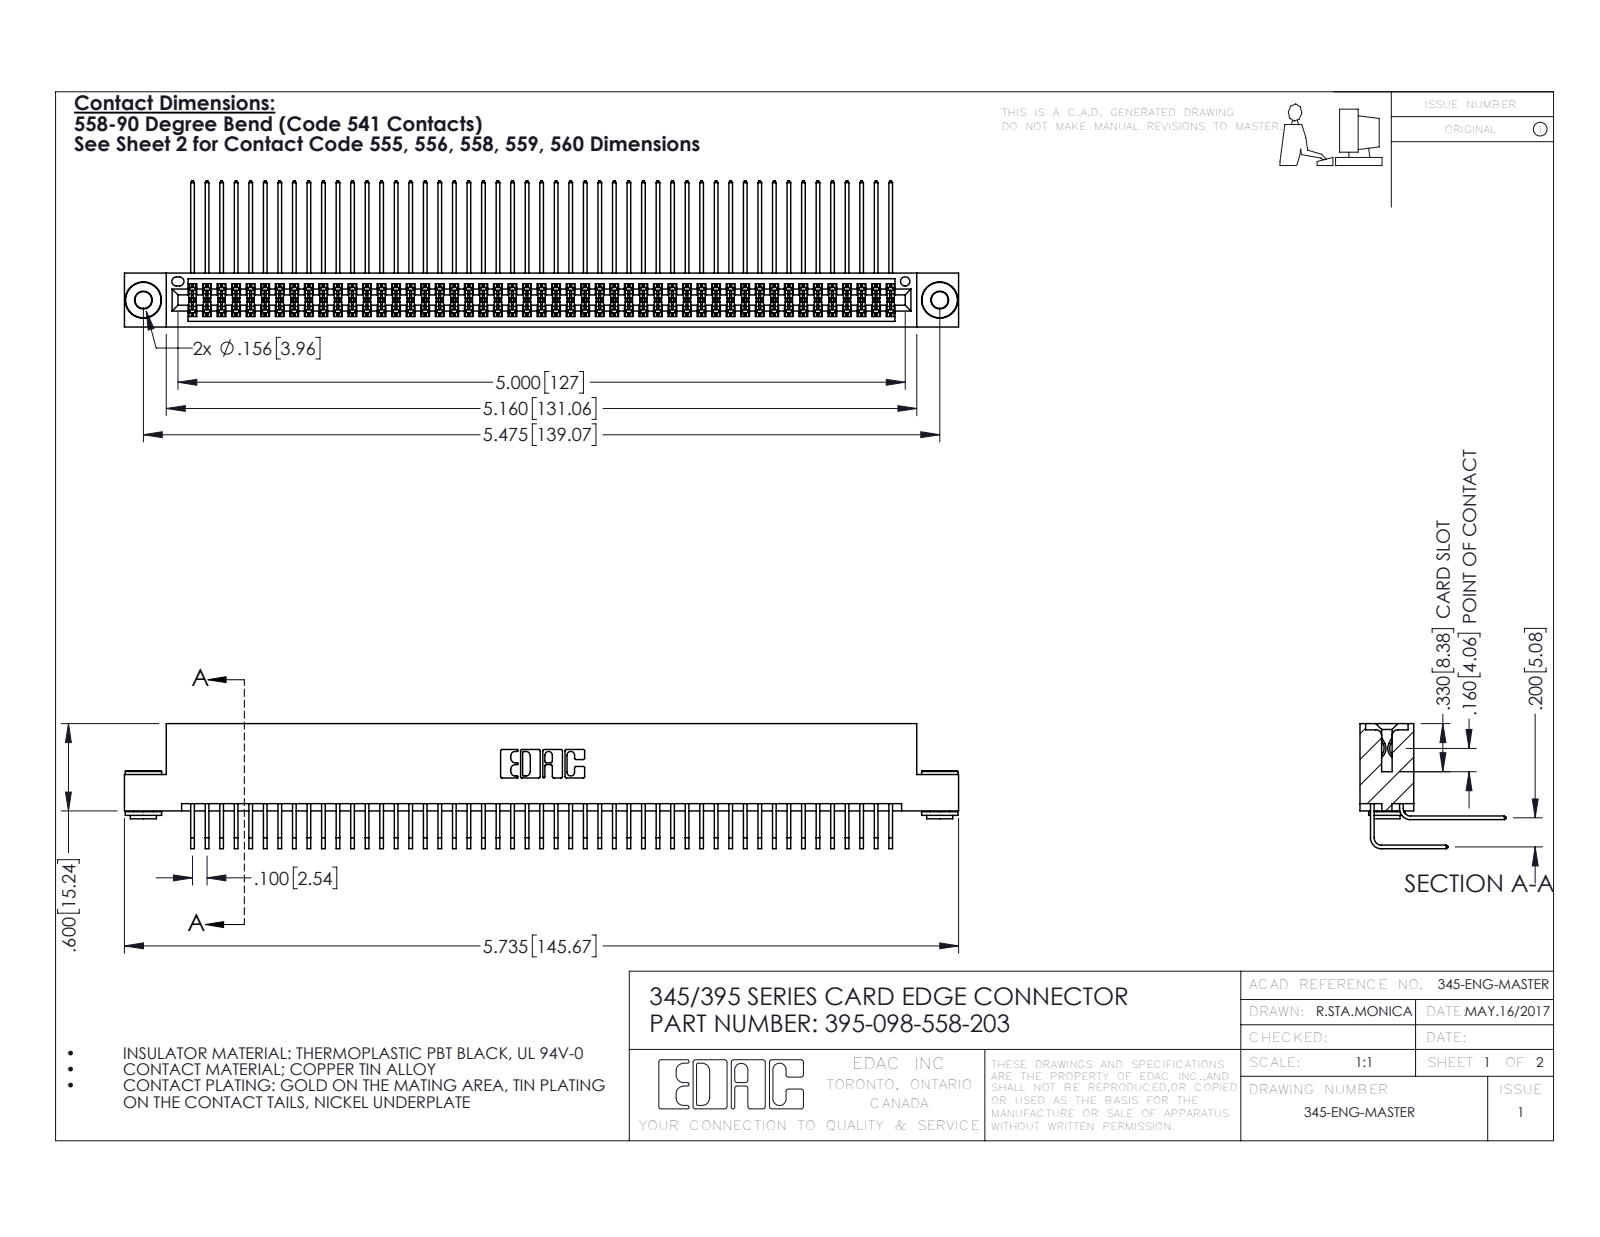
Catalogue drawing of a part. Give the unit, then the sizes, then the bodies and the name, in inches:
Units: inches
Overall size (bounding box): 5.735 × 1.005 × 0.859
Round holes (diameter × count): ⌀0.116 ×2, ⌀0.156 ×2, ⌀0.064 ×1
Round bosses / shafts (diameter × count): ⌀0.25 ×2, ⌀0.18 ×2, ⌀0.136 ×2
Partial cylindrical surfaces — rounded edges, fillets, slot ends (radius × count): R0.006 ×148, R0.01 ×22, R0.007 ×6, R0.031 ×6, R0.026 ×3, R0.014 ×2, R0.019 ×2, R0.022 ×2
Main face-to-face distances: 0.072, 0.298, 0.2, 0.37, 0.025, 0.098, 0.272, 0.225, 0.025, 0.175
Hole centre spacings: 0.27, 5.239, 5.475
Volume: 0.903 in³ · Surface area: 38.56 in²
Bodies: 101 solids, 5260 faces (3520 planar, 1732 cylindrical, 8 other)
Part name (STEP PRODUCT): 345 Part_Flush Mounting Lugs - 0.156 Dia-TH; 395-098-558-203; 345-250-002_345-250-002-102; 345-292-001_558 559 Tail - 1 (+1 more)
STEP written by: SolidWorks 2016 (CONFIG_CONTROL_DESIGN)
